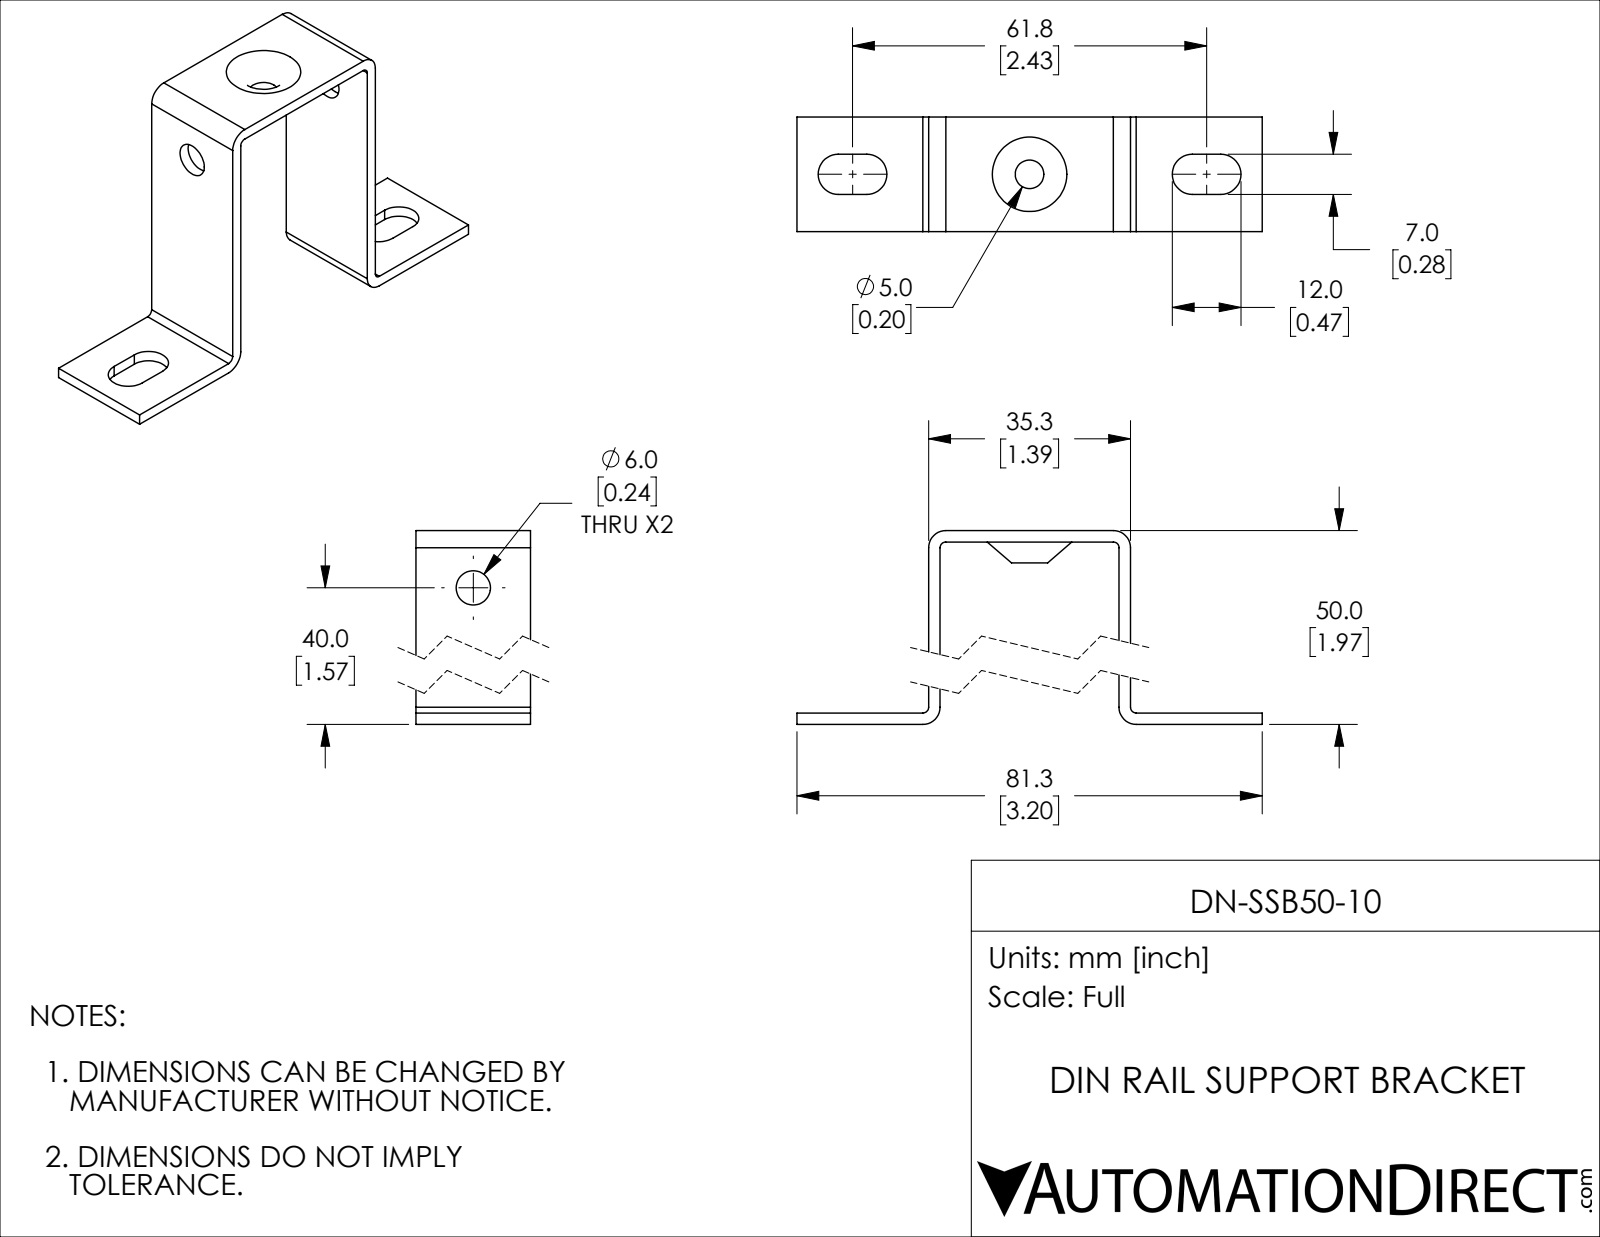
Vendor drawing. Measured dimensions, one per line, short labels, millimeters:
name: DN-SSB50-10
written by: SolidWorks 2018 (AUTOMOTIVE_DESIGN)
unit: mm
bodies: 1 solid, 43 faces (19 planar, 20 cylindrical, 4 other)
size: 81.25 × 50 × 20
volume: 6 698 mm³; area: 7 599 mm²
holes: 1× ⌀5, 1× ⌀6
rounds: 4× R1, 4× R3, 4× R3.5
face distances: 2, 33.24, 48, 35.24, 31.24, 50, 46, 20, 23, 25
